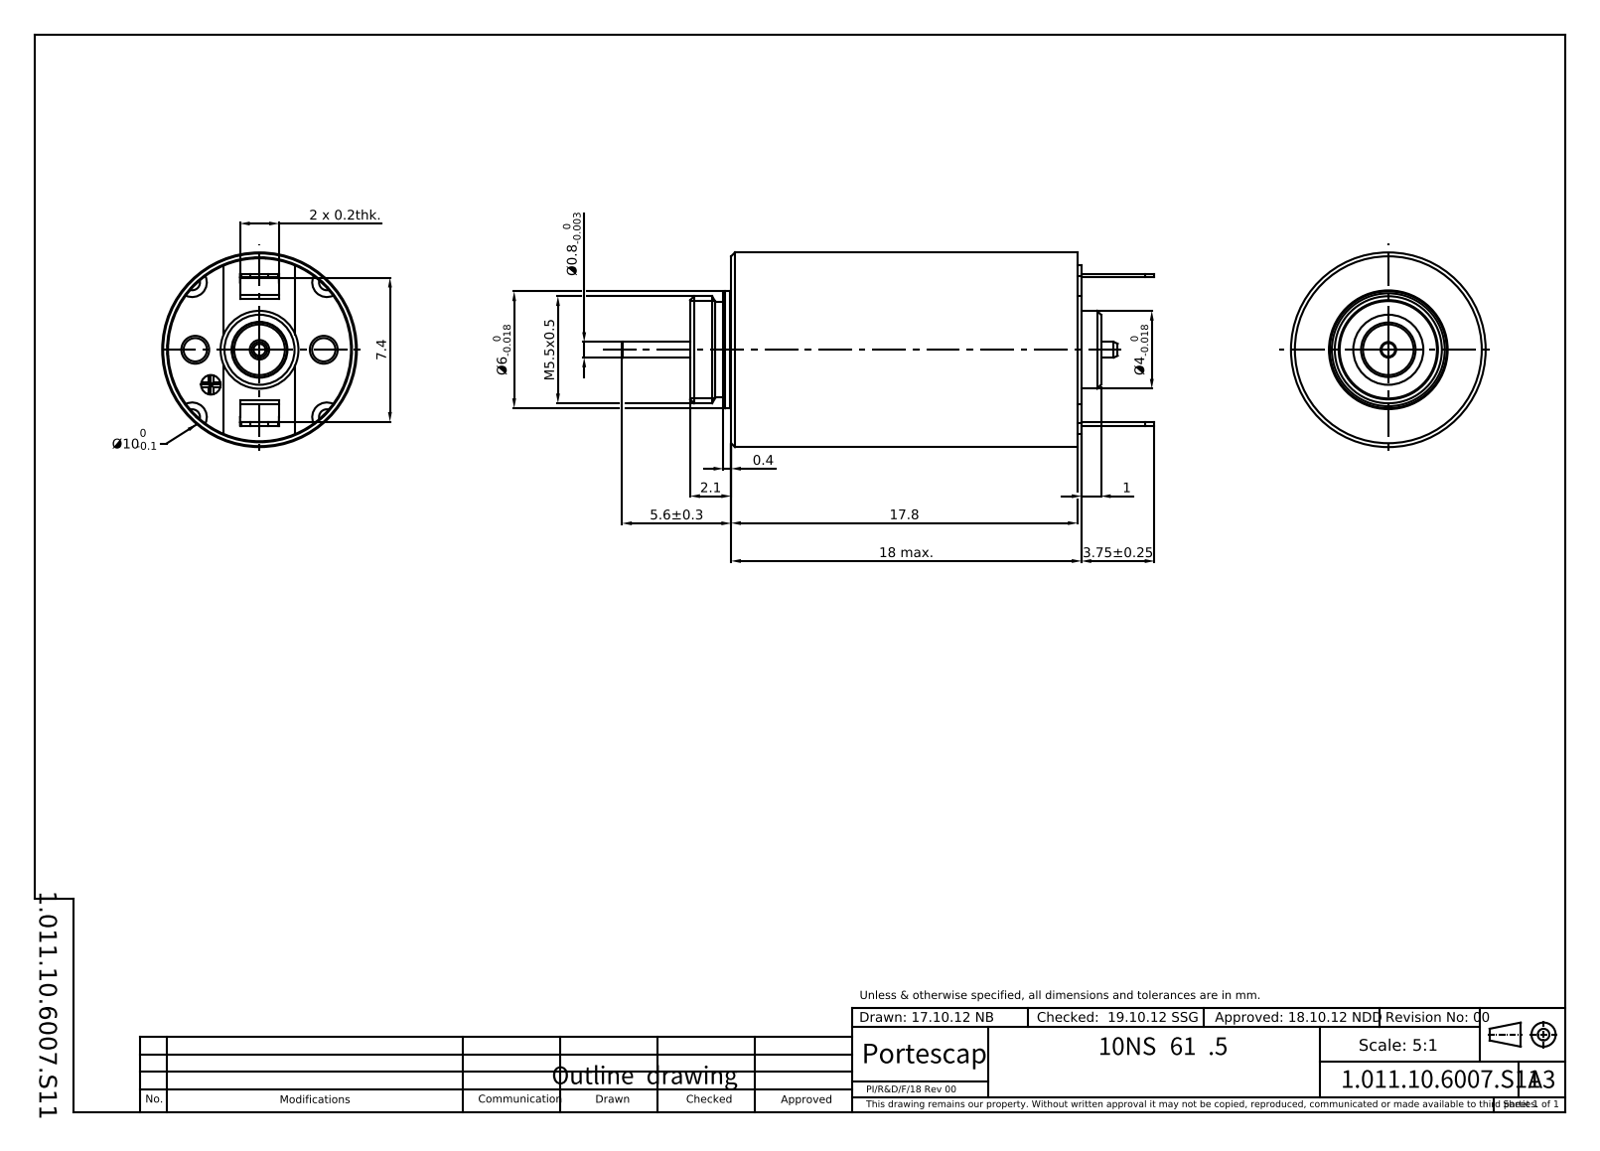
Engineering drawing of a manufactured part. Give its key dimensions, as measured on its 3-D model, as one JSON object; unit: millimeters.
{"part_name": "10NS_61_105C_5", "step_written_by": "PRO/ENGINEER BY PARAMETRIC TECHNOLOGY CORPORATION, 2014310 (CONFIG_CONTROL_DESIGN)", "units": "millimeters", "bodies": {"solids": 1, "faces": 157, "planar": 79, "cylindrical": 48, "other": 30}, "overall_size": [27.35, 10, 10], "volume_mm3": 1457, "surface_area_mm2": 1018, "round_holes": [[1.2, 2], [1, 1], [9.5, 1]], "round_bosses_or_shafts": [[10, 1], [9.4, 1], [6, 1], [5.5, 1], [4.9, 1], [4, 1], [0.8, 1]], "partial_cylinders_radius": [[0.5, 10], [0.15, 4], [0.75, 4]], "face_to_face_distances": [18, 17.7, 1.7, 0.4, 7.6, 20.1, 19.8, 2.1, 18.1, 1.3], "hole_center_spacings": [3.3, 1.97, 3.08, 6.07, 6.6]}
